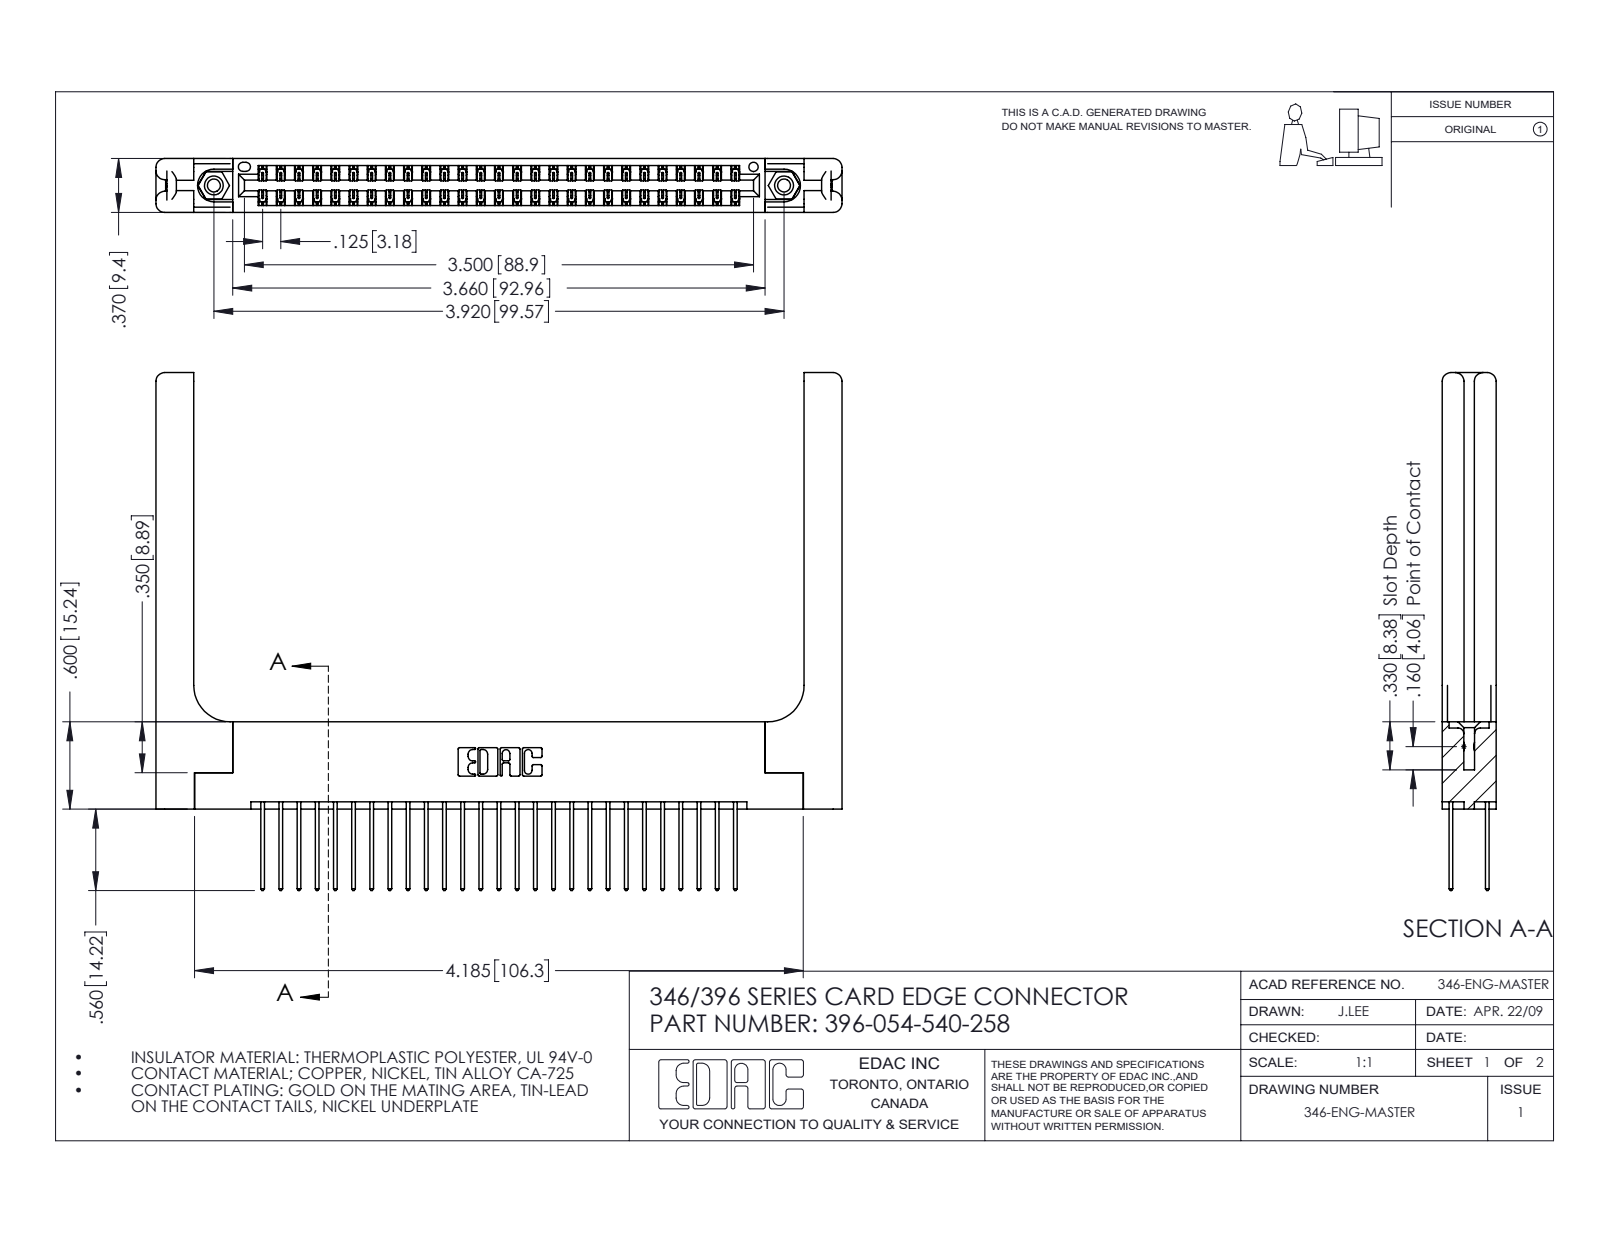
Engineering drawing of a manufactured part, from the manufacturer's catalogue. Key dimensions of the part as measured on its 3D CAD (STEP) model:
Part name (STEP PRODUCT): 345-292-001_345-293-140; 346-220-058_345-220-058; 345-250-001_345-250-001-102; 346 Part_Flush Mounting Lugs - 0.156 Dia-TH (+1 more)
STEP written by: SolidWorks 2016 (CONFIG_CONTROL_DESIGN)
Units: inches
Bodies: 59 solids, 3186 faces (2114 planar, 1012 cylindrical, 60 other)
Overall size (bounding box): 4.716 × 3.56 × 0.37
Volume: 1.176 in³ · Surface area: 33.92 in²
Round holes (diameter × count): ⌀0.089 ×2, ⌀0.125 ×2, ⌀0.156 ×2, ⌀0.064 ×1
Round bosses / shafts (diameter × count): ⌀0.155 ×2
Partial cylindrical surfaces — rounded edges, fillets, slot ends (radius × count): R0.006 ×81, R0.01 ×54, R0.01 ×22, R0.06 ×16, R0.007 ×6, R0.031 ×6, R0.026 ×3, R0.014 ×2
Main face-to-face distances: 0.37, 0.072, 0.048, 0.322, 0.25, 0.148, 0.15, 0.025, 0.298, 0.275
Hole centre spacings: 0.246, 3.712, 3.92
